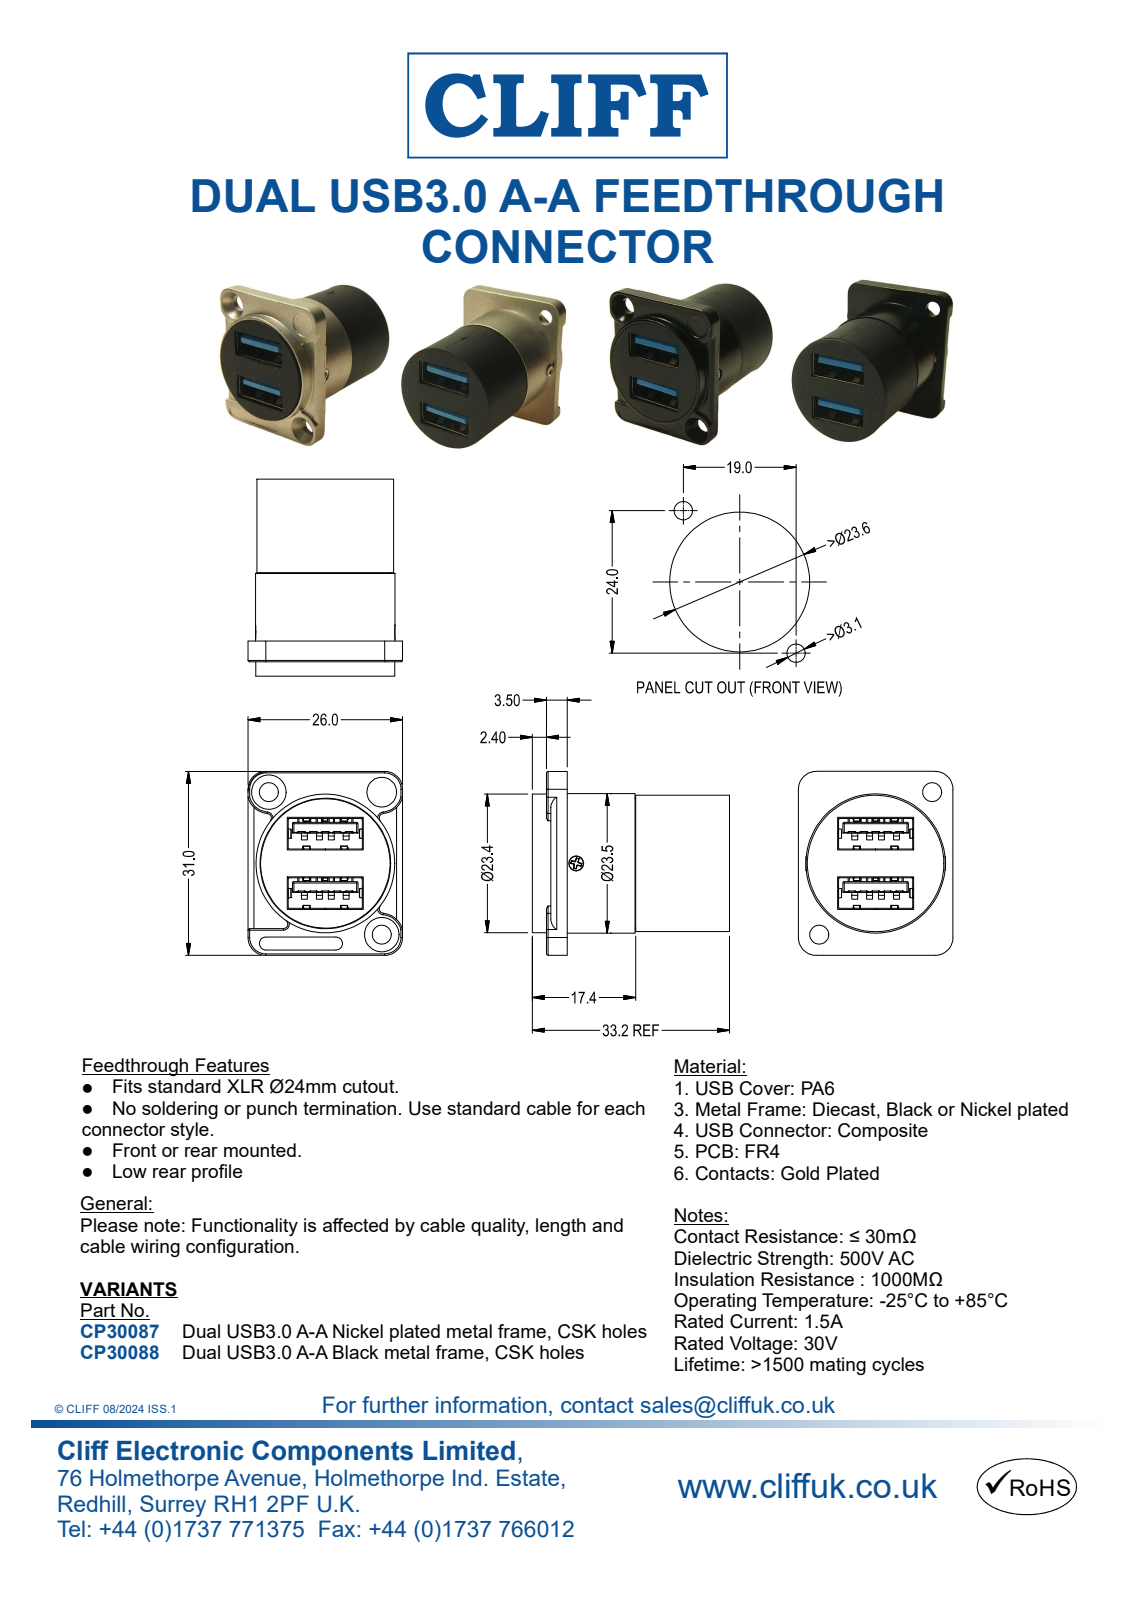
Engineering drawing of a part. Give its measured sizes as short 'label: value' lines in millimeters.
written by: Autodesk Inventor 2022 (AUTOMOTIVE_DESIGN)
unit: mm
bodies: 2 solids, 3210 faces (2401 planar, 791 cylindrical, 18 other)
size: 33.2 × 31 × 26
volume: 9 230 mm³; area: 15 836 mm²
holes: 2× ⌀3.2, 1× ⌀2.5, 1× ⌀5, 1× ⌀22
bosses: 1× ⌀23.5, 1× ⌀23.4, 1× ⌀23, 1× ⌀21.8, 1× ⌀2.4, 1× ⌀1.5
rounds: 216× R0.1, 20× R0.31, 20× R0.5, 16× R0.3, 12× R0.2, 12× R0.61, 10× R0.25, 8× R0.4
face distances: 10, 5.42, 5.86, 1.5, 10.14, 15.86, 1.8, 13.76, 10.3, 9.7
hole spacings: 15.31, 19, 24, 30.61
